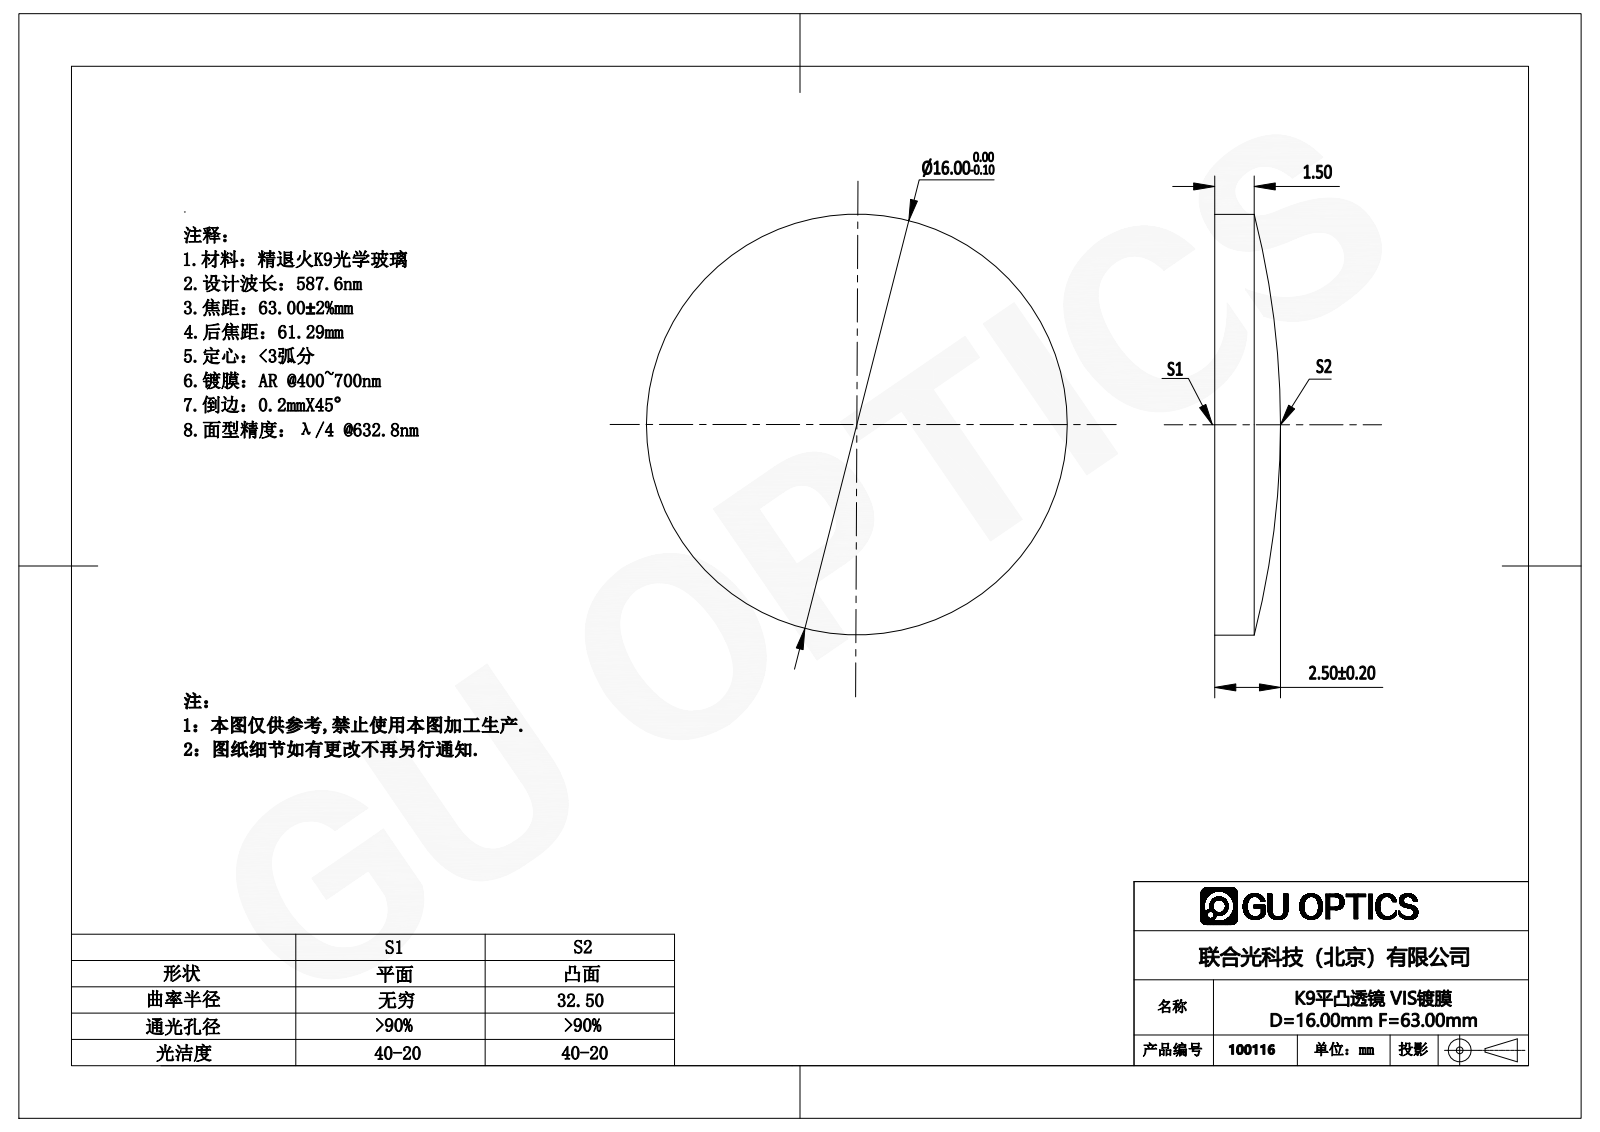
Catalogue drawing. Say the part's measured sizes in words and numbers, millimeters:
The part is named "100116". Its 3-D file was written by "SolidWorks 2016 (AUTOMOTIVE_DESIGN)". It is 1 solid with 5 faces: 1 planar, 2 cylindrical and 2 other. Overall it measures 16 by 16 by 2.5 millimeters. Its volume is 403 cubic millimeters and its surface area 481 square millimeters. Round bosses or shafts: 1 of diameter 16.
